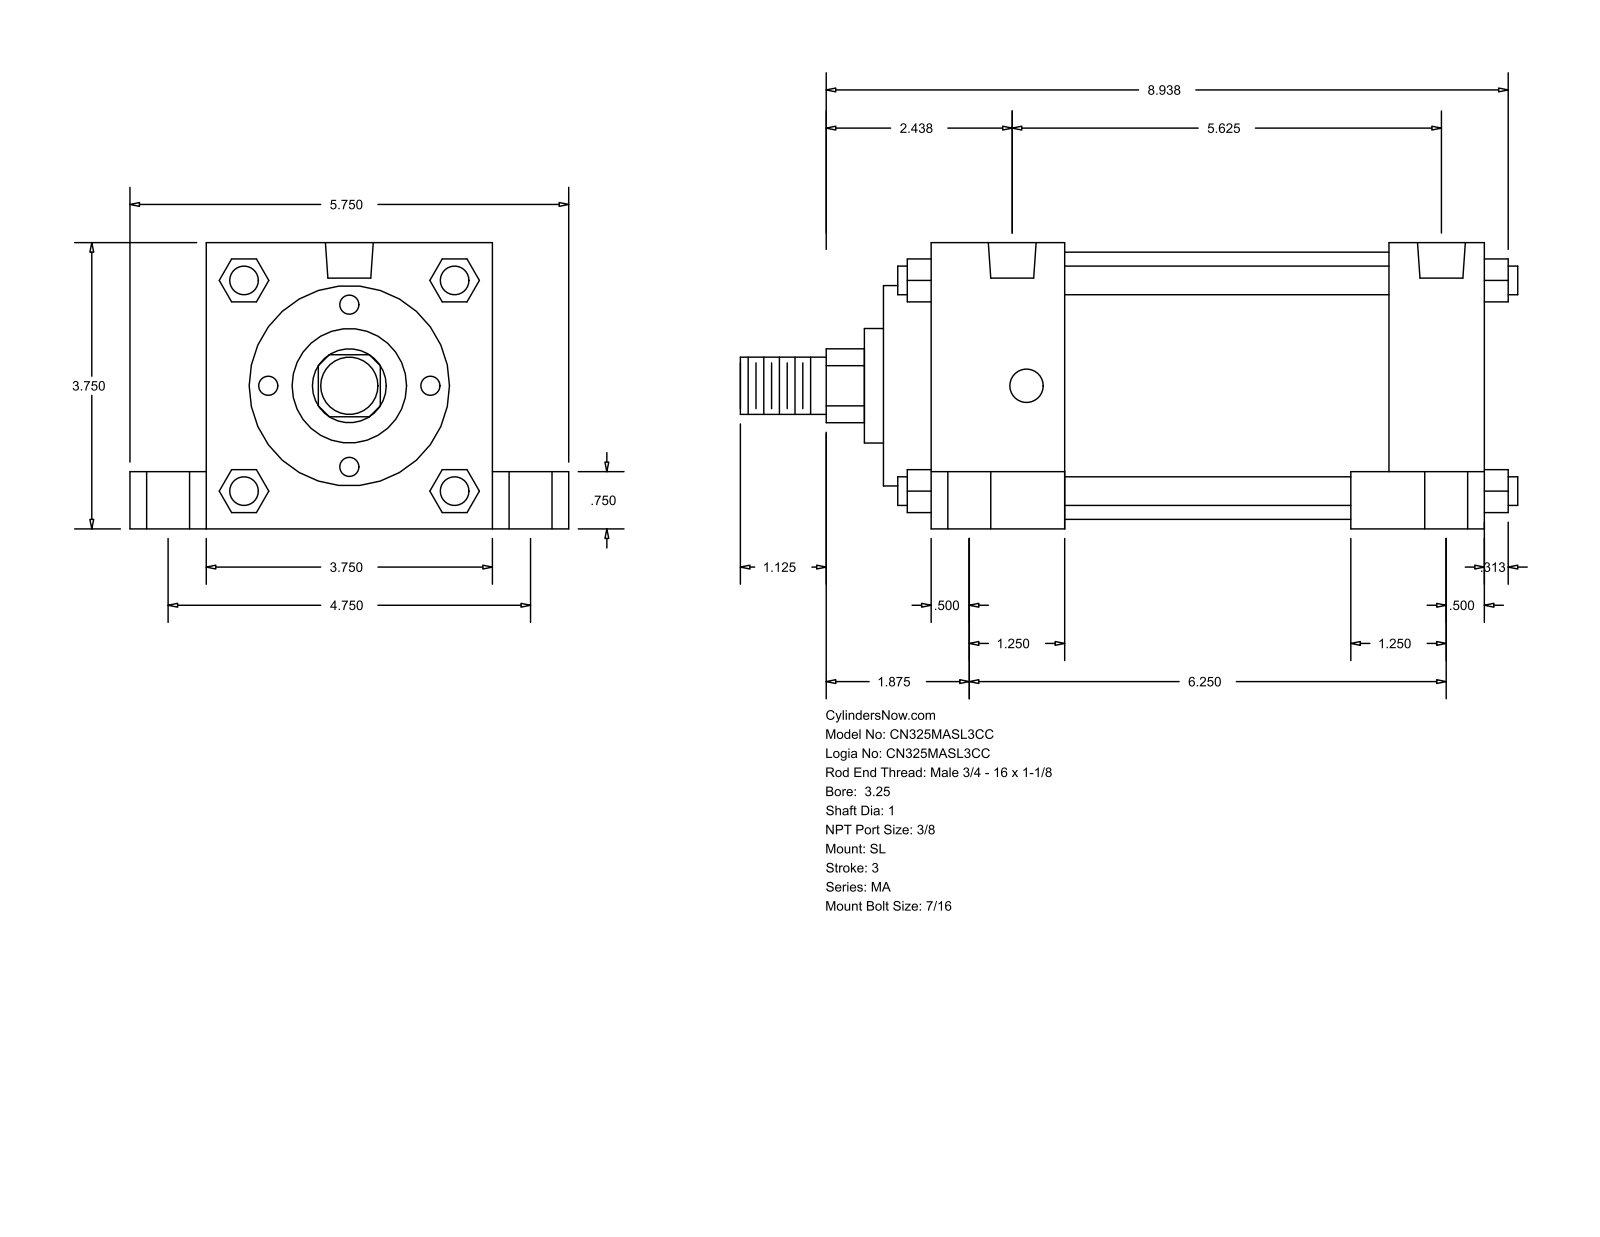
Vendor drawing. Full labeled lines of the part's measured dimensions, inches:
Part name (STEP PRODUCT): MA_SL__0325_1
STEP written by: GSSL Pune (CONFIG_CONTROL_DESIGN)
Units: inches
Bodies: 0 solids, 150 faces (113 planar, 37 cylindrical, 0 other)
Overall size (bounding box): 10.187 × 5.75 × 3.75
Round holes (diameter × count): ⌀0.437 ×4, ⌀0.563 ×4, ⌀0.813 ×4, ⌀0.627 ×2
Round bosses / shafts (diameter × count): ⌀0.375 ×4, ⌀3.5 ×1, ⌀2.625 ×1, ⌀1.5 ×1, ⌀1 ×1, ⌀0.75 ×1
Partial cylindrical surfaces — rounded edges, fillets, slot ends (radius × count): R0.484 ×1
Main face-to-face distances: 3.75, 7.25, 0.625, 1, 4.75, 7.875, 0.75, 6, 1.25, 1.75
Hole centre spacings: 0.187, 2.376, 2.388, 2.441, 2.491, 4.75, 5.25, 5.438
